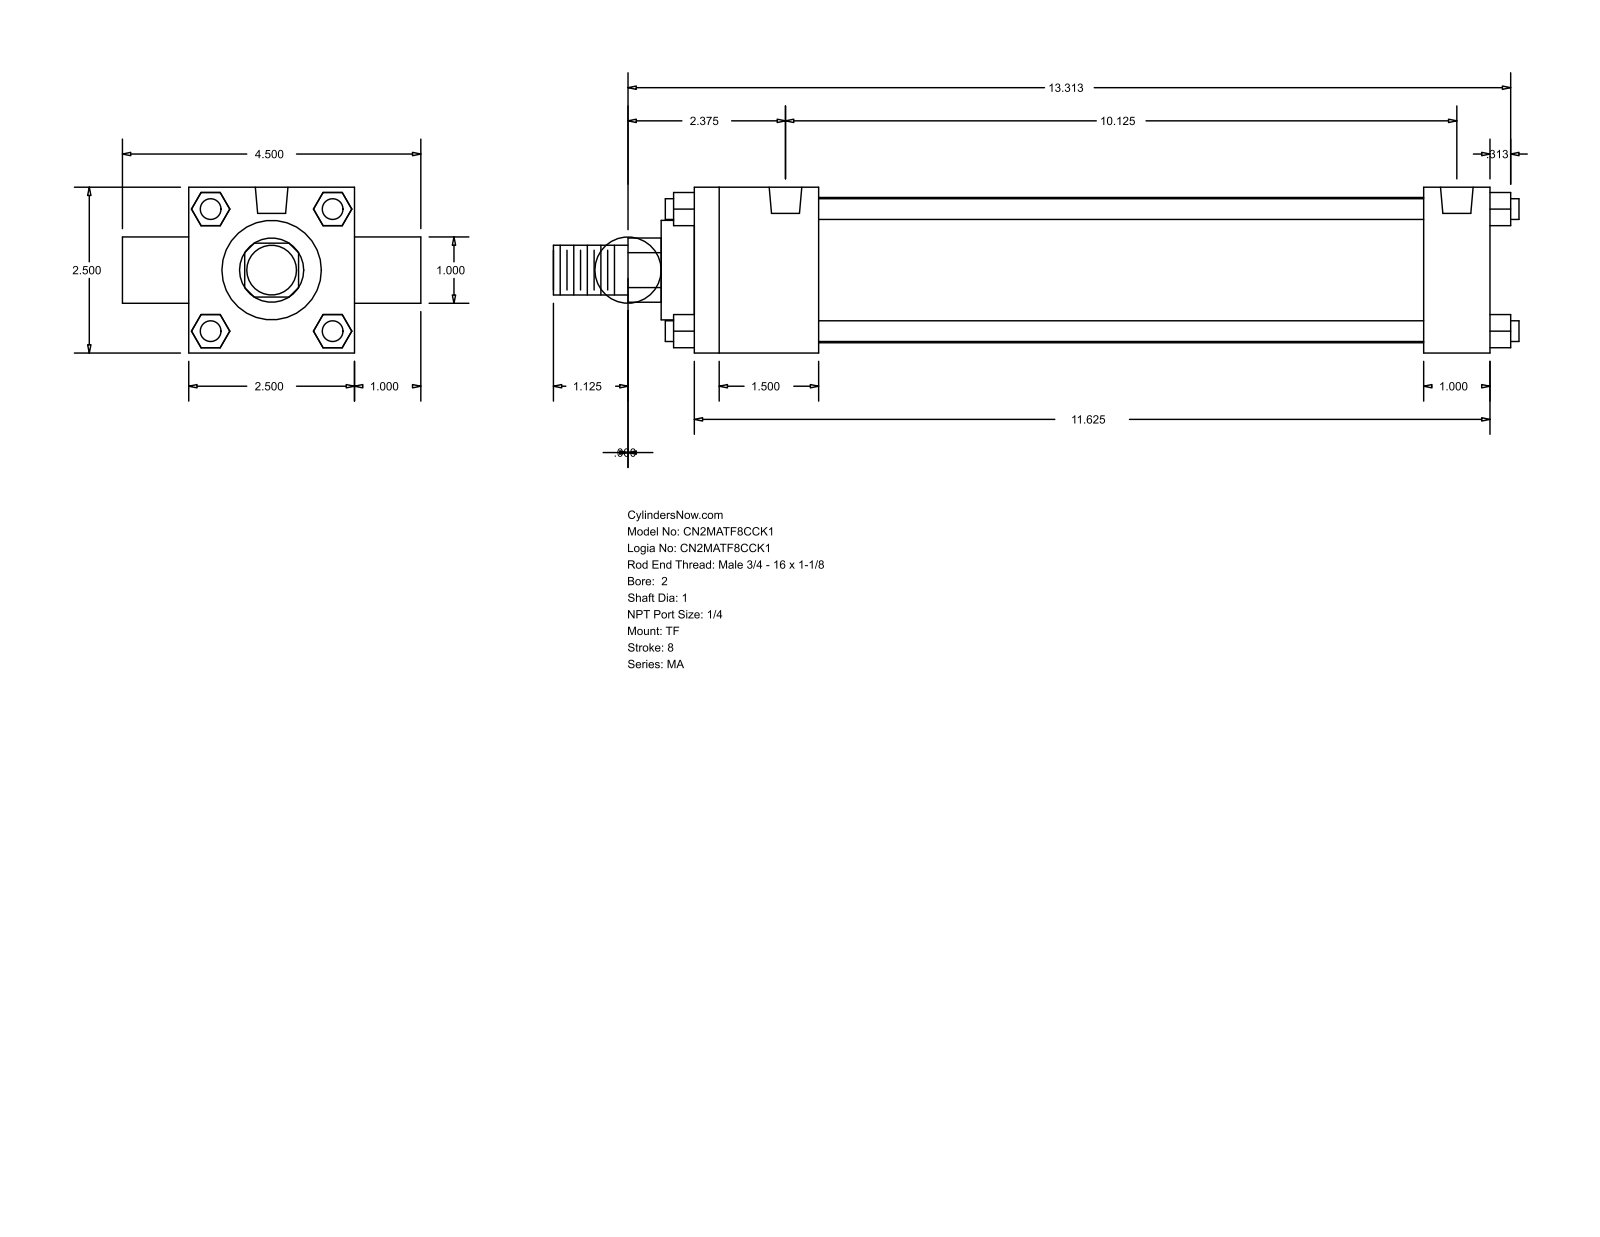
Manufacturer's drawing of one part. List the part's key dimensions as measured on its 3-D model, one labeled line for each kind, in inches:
Part name (STEP PRODUCT): MA_TF__0200_1
STEP written by: GSSL Pune (CONFIG_CONTROL_DESIGN)
Units: inches
Bodies: 0 solids, 120 faces (92 planar, 28 cylindrical, 0 other)
Overall size (bounding box): 14.563 × 4.5 × 2.5
Round holes (diameter × count): ⌀0.313 ×3, ⌀0.492 ×2
Round bosses / shafts (diameter × count): ⌀0.313 ×4, ⌀1 ×2, ⌀2.19 ×1, ⌀1.5 ×1, ⌀0.75 ×1
Partial cylindrical surfaces — rounded edges, fillets, slot ends (radius × count): R0.484 ×1
Main face-to-face distances: 2.5, 1, 12, 0.5, 1.875, 11, 9.125, 10.125, 3.5, 1.593
Hole centre spacings: 10.125
